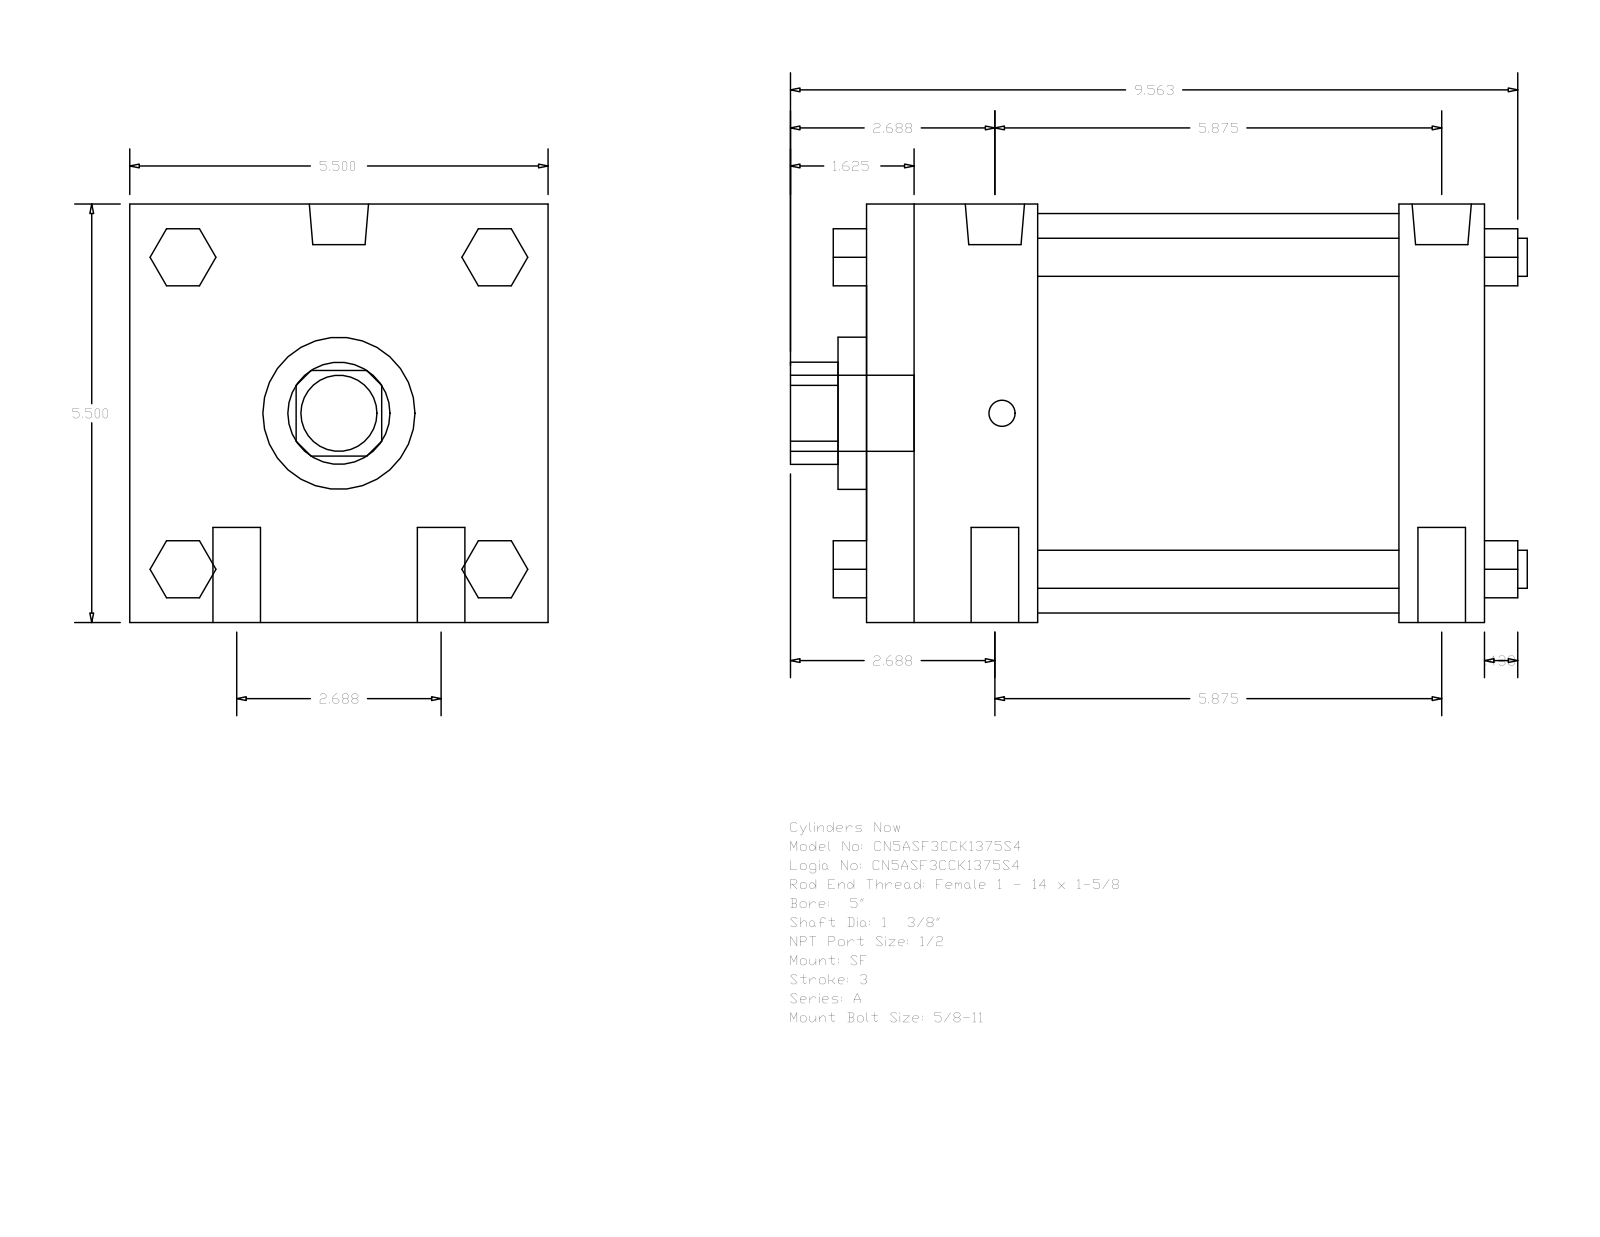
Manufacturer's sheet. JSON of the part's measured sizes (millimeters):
{"part_name": "A_SF__0500_1.375", "step_written_by": "GSSL Pune (CONFIG_CONTROL_DESIGN)", "units": "millimeters", "bodies": {"solids": 0, "faces": 124, "planar": 94, "cylindrical": 30, "other": 0}, "overall_size": [246.06, 139.7, 139.7], "round_holes": [[34.92, 1], [50.8, 1], [133.35, 1]], "round_bosses_or_shafts": [[15.88, 4], [12.7, 4], [19.77, 2], [8.73, 2], [25.4, 1]], "partial_cylinders_radius": [[17.06, 1]], "face_to_face_distances": [139.7, 206.38, 28.58, 57.15, 177.8, 120.65, 149.23, 19.05, 52.07, 90.18]}
